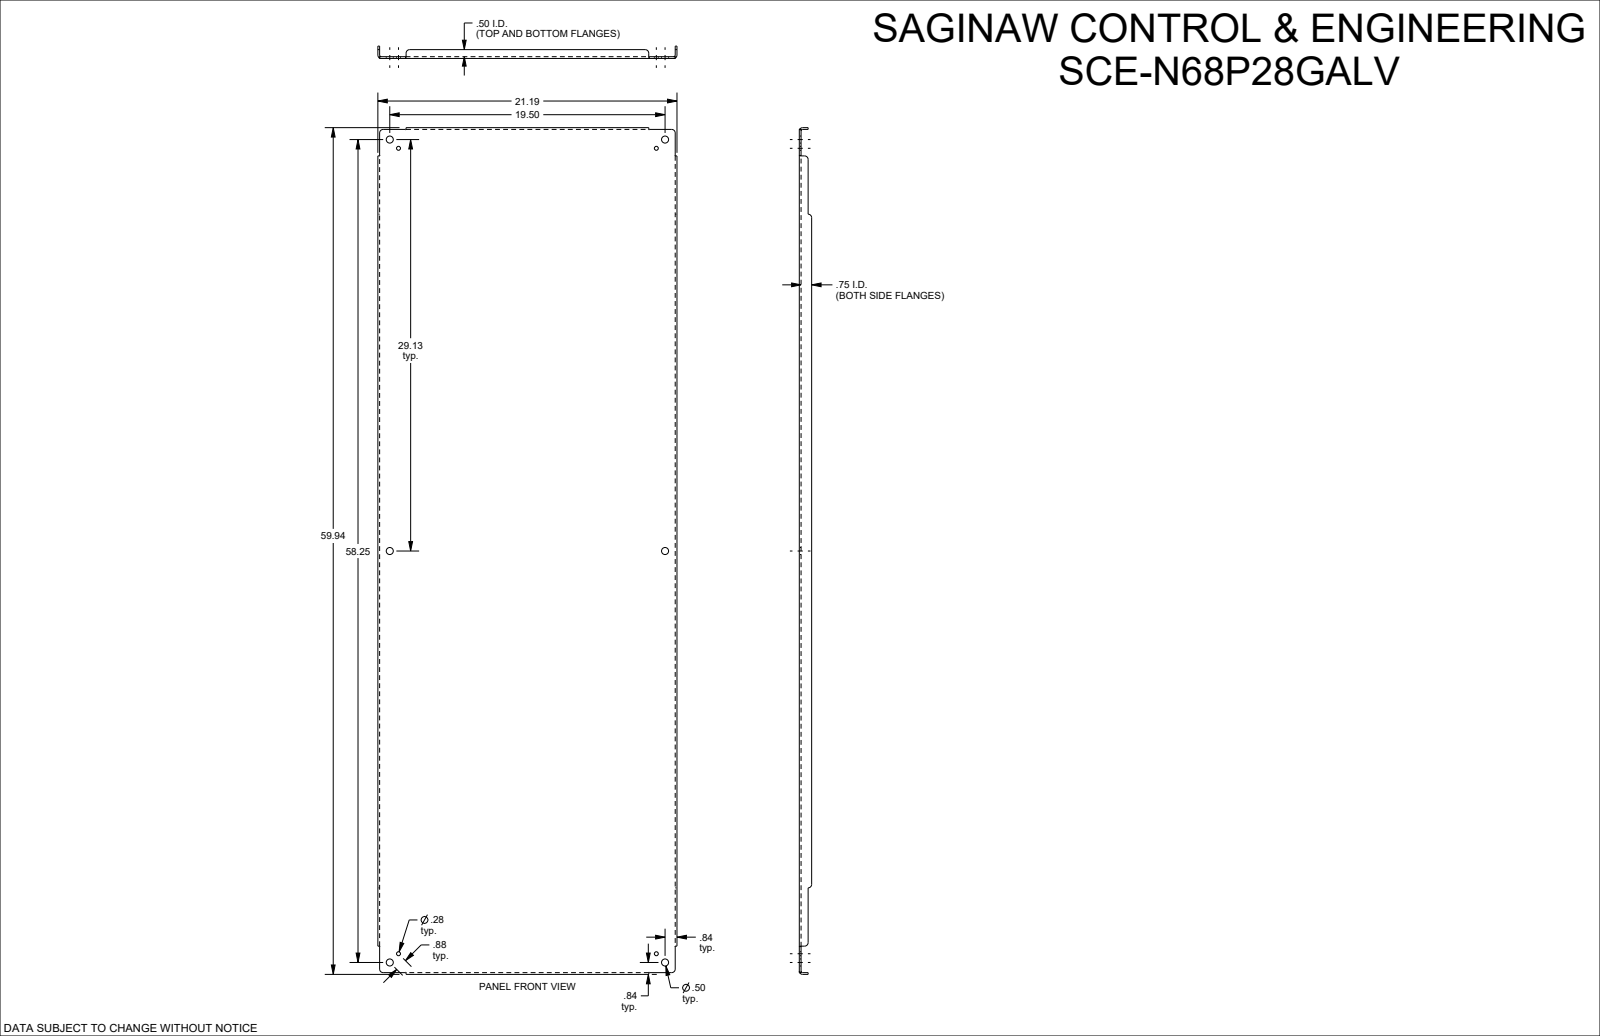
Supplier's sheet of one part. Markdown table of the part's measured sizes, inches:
| quantity | value |
| --- | --- |
| part name | SCE-N68P28GALV |
| STEP written by | SolidWorks 2023 (AUTOMOTIVE_DESIGN) |
| units | inches |
| bodies | 1 solid, 110 faces (42 planar, 44 cylindrical, 24 other) |
| overall size | 59.938 × 21.188 × 0.875 |
| volume | 169 in³ |
| surface area | 2 727 in² |
| round holes (diameter × count) | 0.5 × 6, 0.281 × 4 |
| partial cylindrical surfaces (radius × count) | 0.25 × 11, 0.112 × 4, 0.237 × 4 |
| main face-to-face distances | 0.125, 21.063, 20.938, 21.187, 0.125, 59.813, 0.75, 0.875, 59.687, 59.938 |
| hole center spacings | 0.875, 18.891, 28.513, 29.125, 34.192, 35.05, 57.634, 60.645 |
